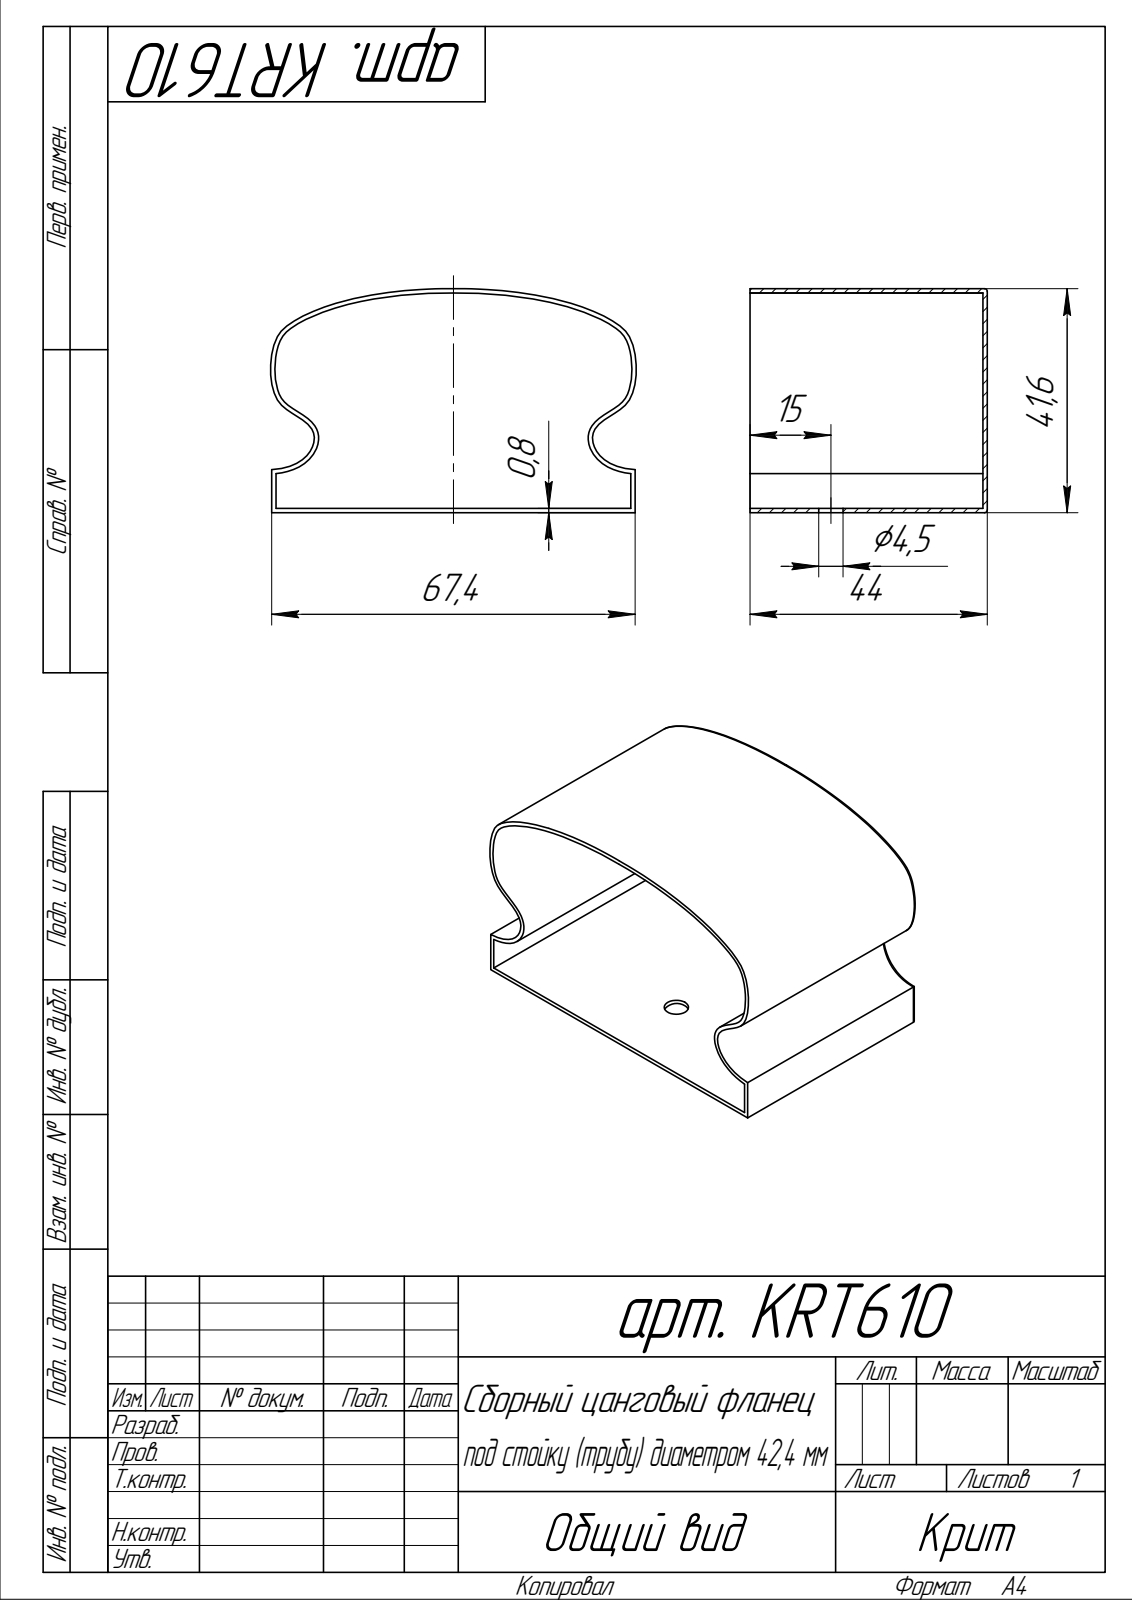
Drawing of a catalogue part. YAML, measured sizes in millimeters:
part_name: "арт. KRT610"
step_written_by: "SolidWorks 2014 (AUTOMOTIVE_DESIGN)"
units: millimeters
bodies: {solids: 1, faces: 20, planar: 9, cylindrical: 5, other: 6}
overall_size: [67.85, 44, 41.6]
volume: 10363
surface_area: 23771
round_holes:
  - {diameter: 4.5, count: 1}
partial_cylinders:
  - {radius: 0.5, count: 3}
face_to_face_distances: [0.8, 66.6, 67.4, 65.8, 44, 43.2]
